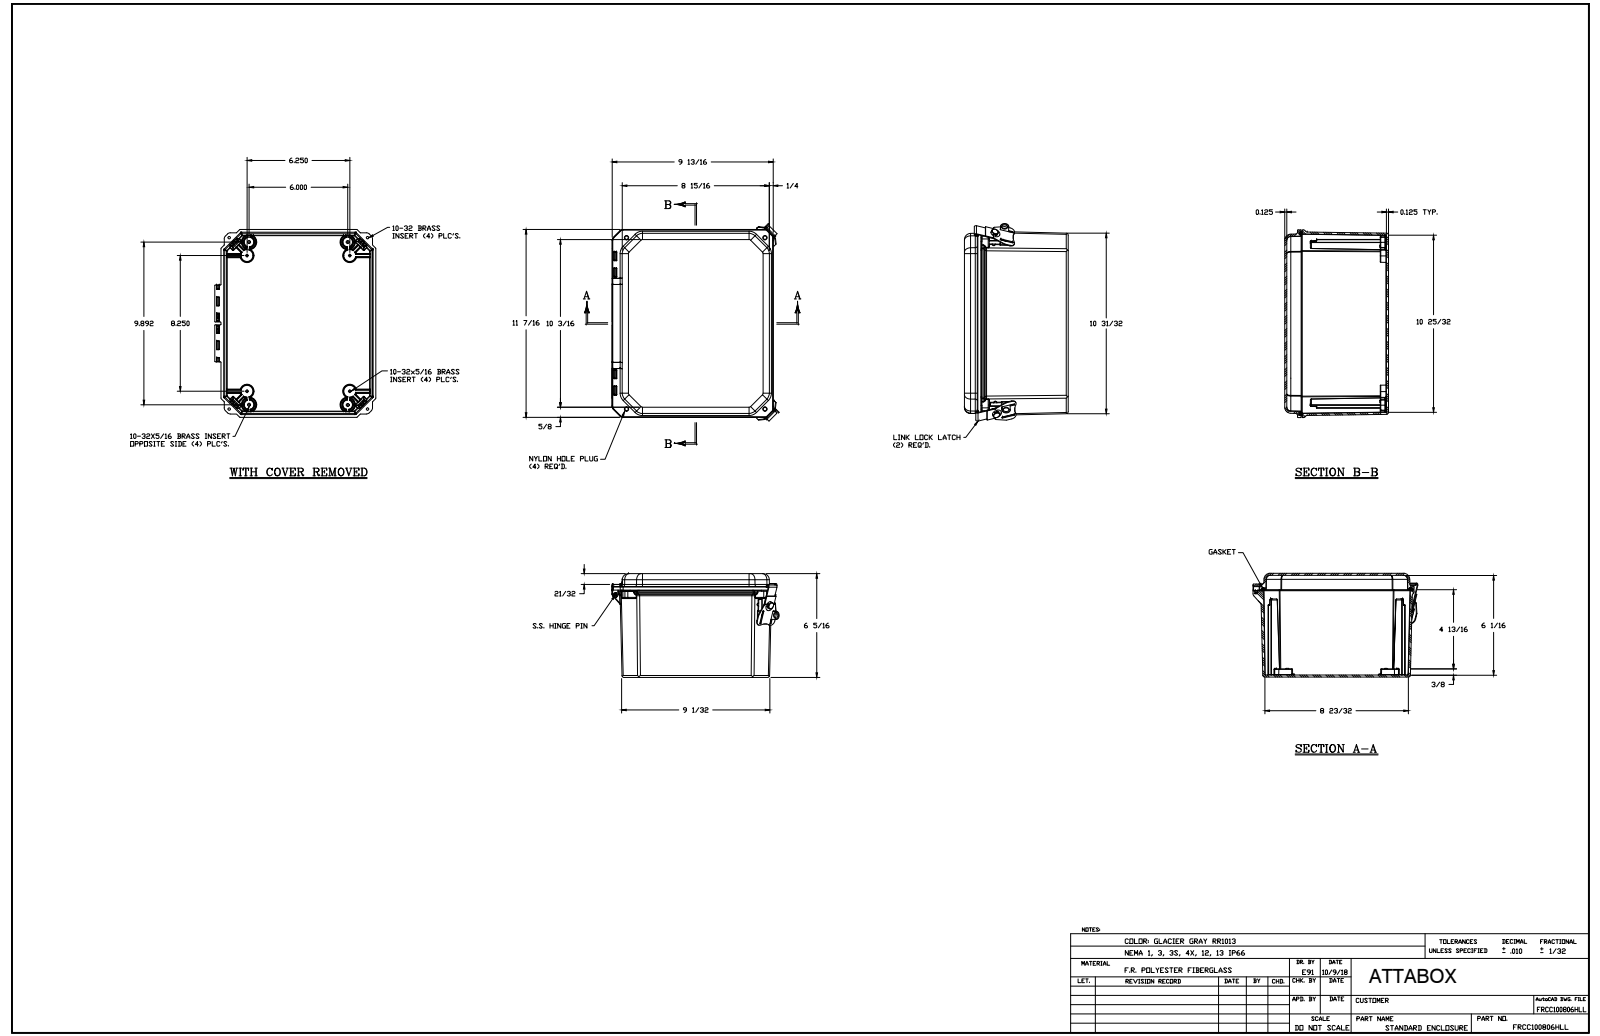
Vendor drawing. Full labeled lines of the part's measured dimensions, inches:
Part name (STEP PRODUCT): FRCC100806HLL
STEP written by: SolidWorks 2018 (AUTOMOTIVE_DESIGN)
Units: inches
Bodies: 33 solids, 2260 faces (656 planar, 890 cylindrical, 714 other)
Overall size (bounding box): 12.33 × 10.254 × 6.312
Volume: 63.38 in³ · Surface area: 985.9 in²
Round holes (diameter × count): ⌀0.156 ×12, ⌀0.152 ×8, ⌀0.098 ×4, ⌀0.15 ×4, ⌀0.219 ×4, ⌀0.252 ×4, ⌀0.312 ×4, ⌀0.05 ×2, ⌀0.12 ×2, ⌀0.363 ×2, ⌀0.137 ×1
Round bosses / shafts (diameter × count): ⌀0.246 ×12, ⌀0.87 ×4, ⌀0.209 ×4, ⌀0.2 ×4, ⌀0.6 ×2, ⌀0.135 ×2, ⌀0.05 ×2, ⌀0.135 ×1
Partial cylindrical surfaces — rounded edges, fillets, slot ends (radius × count): R0.01 ×208, R0.005 ×94, R0.02 ×59, R0.125 ×41, R0.03 ×38, R0.039 ×28, R0.25 ×26, R0.03 ×24
Main face-to-face distances: 0.125, 6.187, 0.127, 0.126, 6.312, 6.062, 5.531, 0.656, 0.25, 1
Hole centre spacings: 10.422, 0.831, 9.072, 9.399, 10.35, 11.873, 1.536, 8.25
